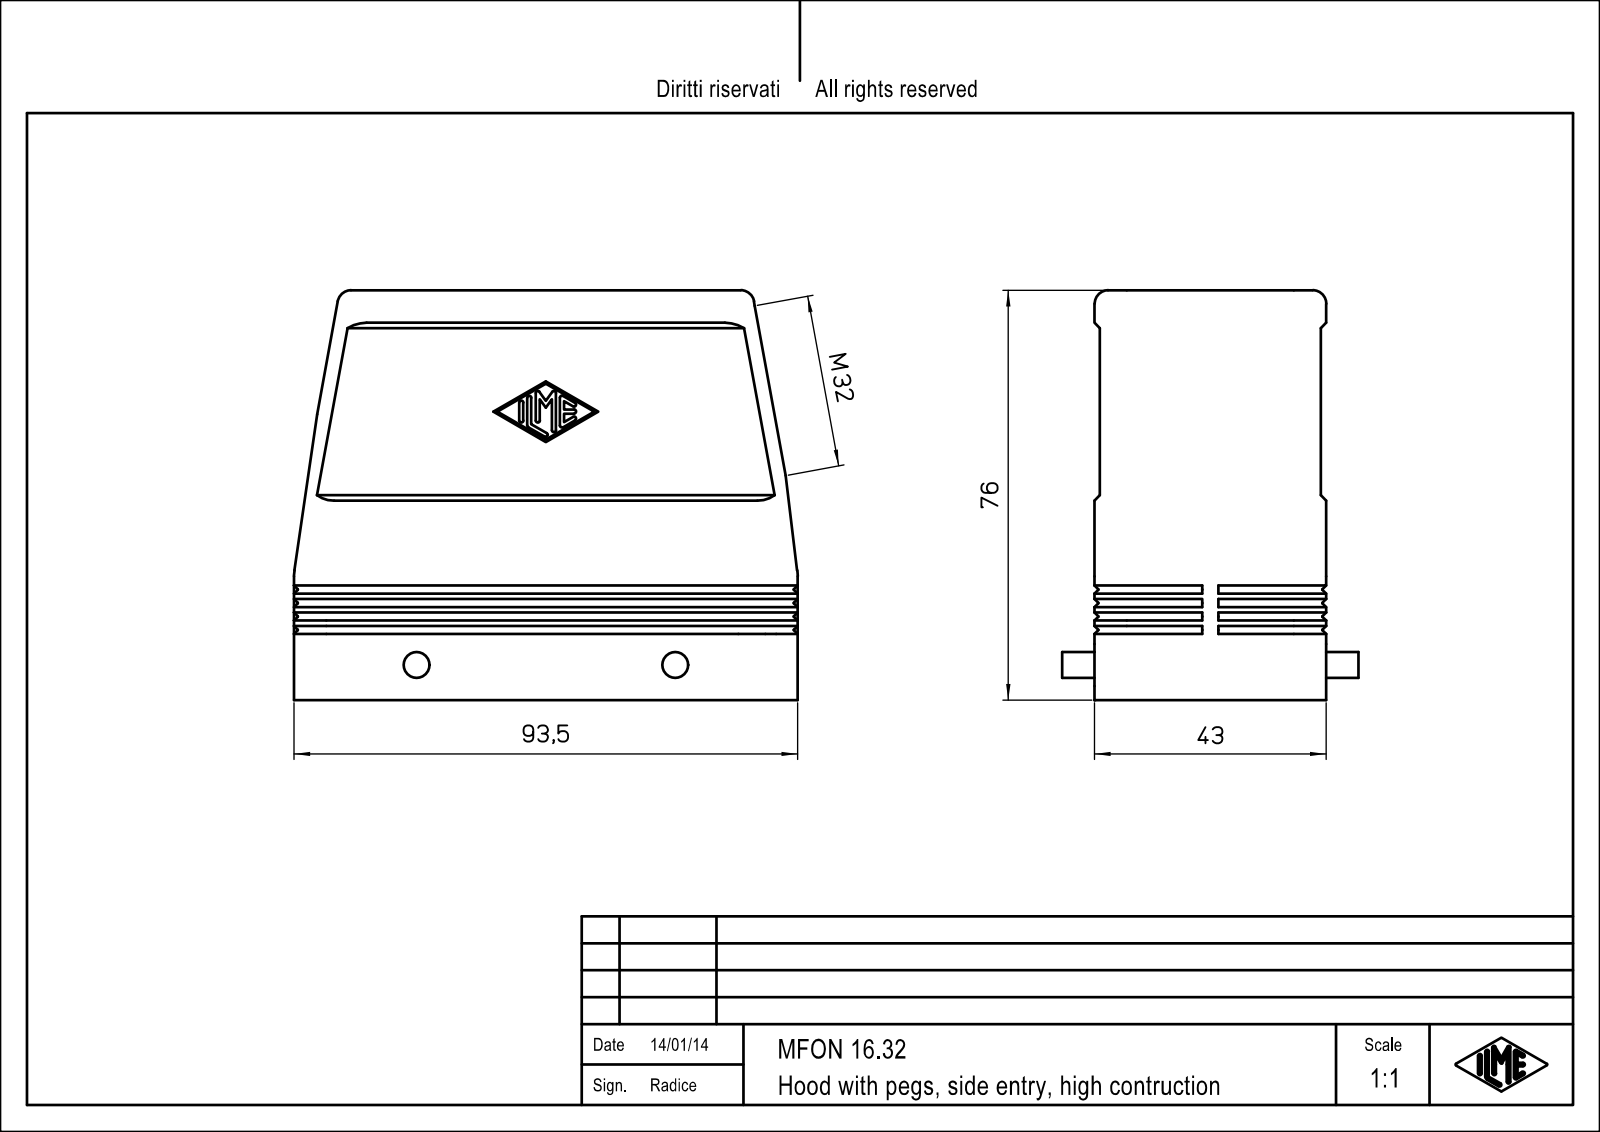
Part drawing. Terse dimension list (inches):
name: MFON_16.32
written by: CoCreate Modeling 16.00A 16-Aug-2008 (C) Parametric Technology GmbH (AUTOMOTIVE_DESIGN)
unit: in
bodies: 0 solids, 640 faces (169 planar, 290 cylindrical, 181 other)
size: 3.681 × 2.992 × 2.169
holes: 4× ⌀0.079, 4× ⌀0.122, 1× ⌀1.26
bosses: 2× ⌀0.189
rounds: 52× R0.008, 24× R0.01, 8× R0.236, 4× R0.059, 4× R0.098, 4× R0.118, 4× R0.787, 1× R0.886
face distances: 0.136, 1.518, 0.138, 0.096, 1.654, 0.039, 1.557, 1.555, 0.098, 1.516
hole spacings: 1.063, 3.051, 3.231
